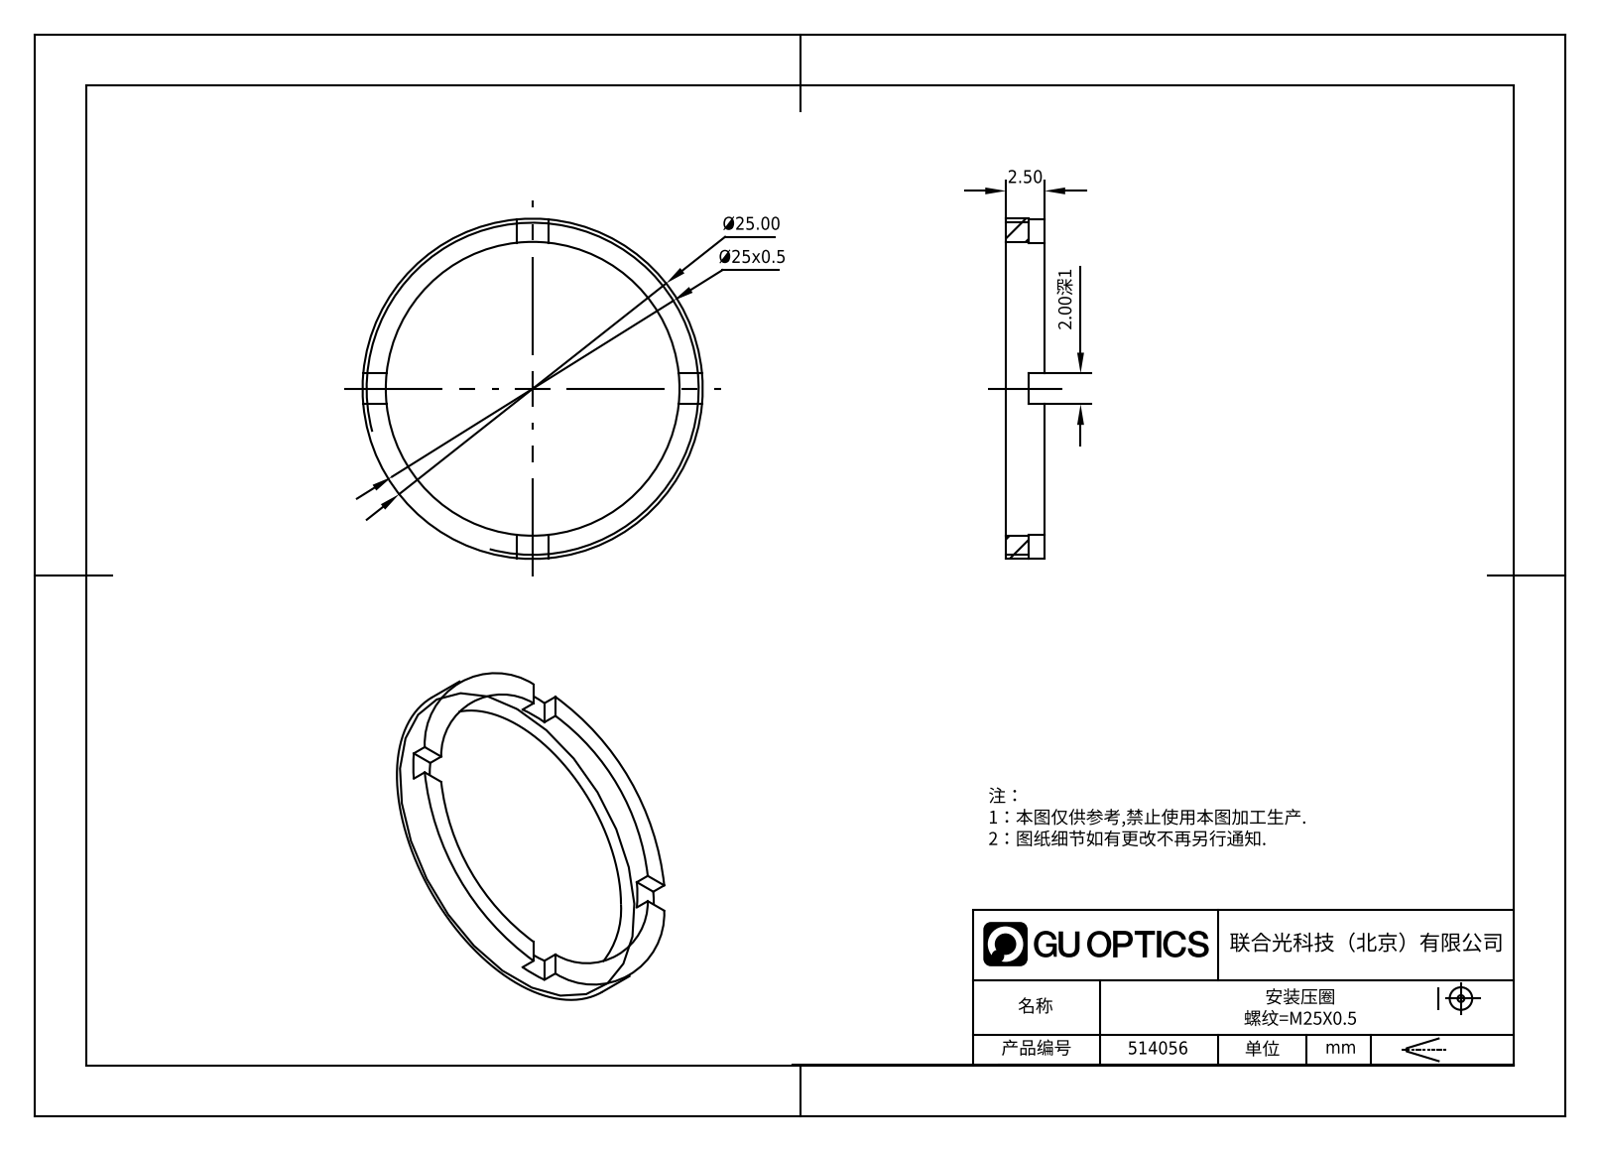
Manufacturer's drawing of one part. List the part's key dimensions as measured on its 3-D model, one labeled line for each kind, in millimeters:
Part name (STEP PRODUCT): 514056
STEP written by: SolidWorks 2020 (CONFIG_CONTROL_DESIGN)
Units: millimetres
Bodies: 1 solid, 21 faces (17 planar, 4 cylindrical, 0 other)
Overall size (bounding box): 25 × 25 × 2.5
Volume: 265 mm³ · Surface area: 587 mm²
Round holes (diameter × count): ⌀22 ×1
Round bosses / shafts (diameter × count): ⌀25 ×1
Main face-to-face distances: 2.5, 1.5, 1, 2
